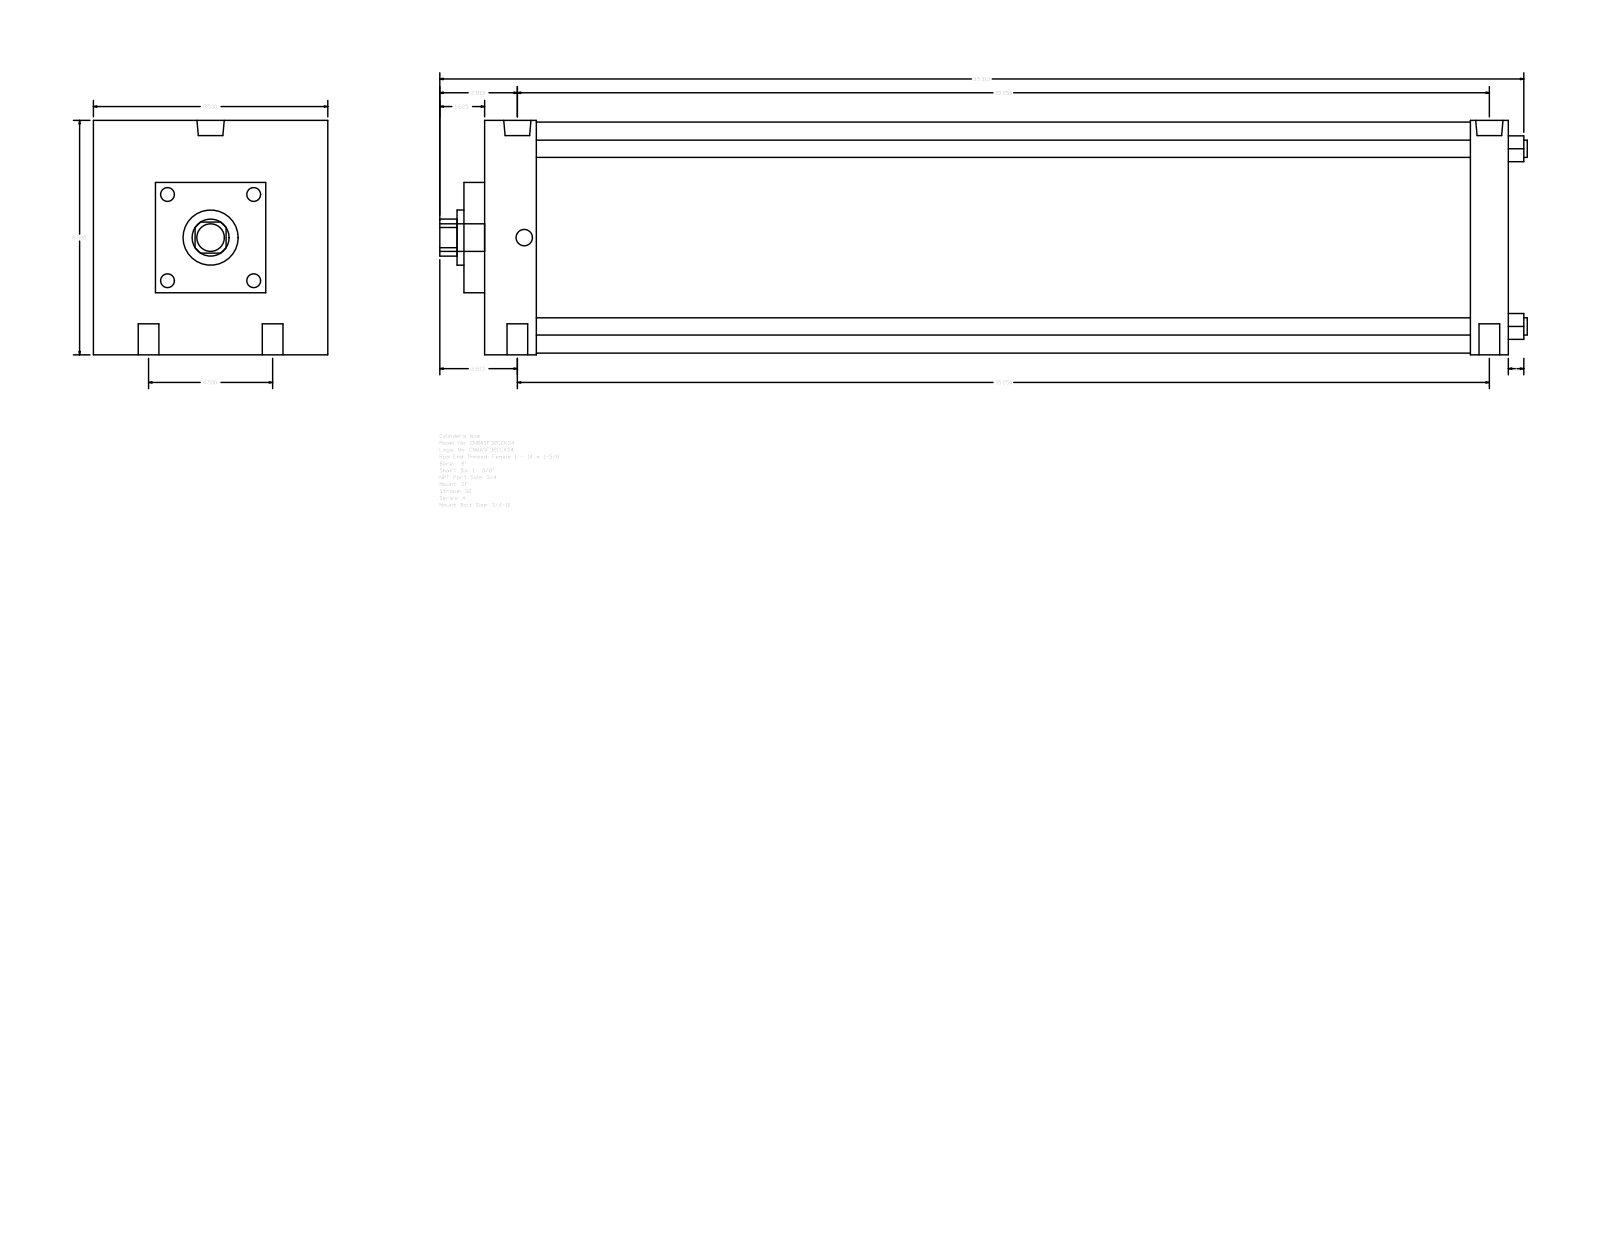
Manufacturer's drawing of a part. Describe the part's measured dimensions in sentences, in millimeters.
The part is named "A_SF__0800_1.375". Its 3-D file was written by "GSSL Pune (CONFIG_CONTROL_DESIGN)". It is 0 solids with 93 faces: 67 planar, 26 cylindrical and 0 other. Overall it measures 1001.71 by 215.9 by 215.9 millimeters. Round holes: 4 of diameter 19.05, 2 of diameter 15.08, 2 of diameter 25.12, 1 of diameter 34.92, 1 of diameter 50.8. Round bosses or shafts: 4 of diameter 15.88, 1 of diameter 212.72, 1 of diameter 25.4. Partial cylindrical surfaces (rounded edges, fillets, slot ends): 1 of radius 17.06. The main face-to-face distances are 942.98, 215.9, 47.63, 908.06, 860.43, 895.35, 34.92, 19.04, 66.67, 927.1. The hole center spacings are 57.15, 897.17, 895.35, 114.3, 902.62, 882.65.
